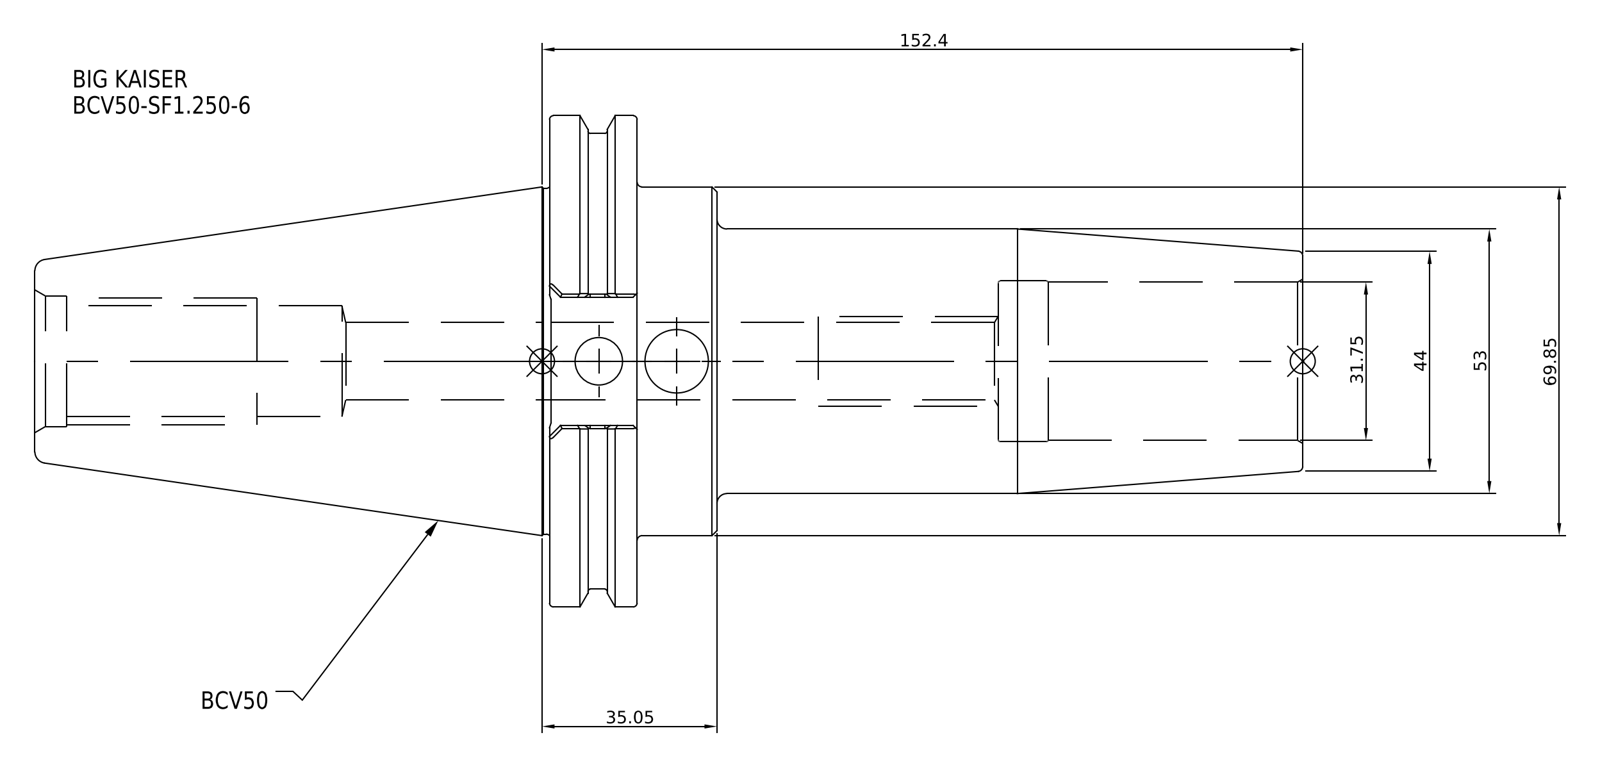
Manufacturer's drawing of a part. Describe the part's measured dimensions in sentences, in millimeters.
The part is named "BCV50-SF1_250-6". Its 3-D file was written by "SolidWorks 2021 (CONFIG_CONTROL_DESIGN)". It is 1 solid with 30 faces: 8 planar, 14 cylindrical and 8 other. Overall it measures 254 by 98.43 by 98.43 millimeters. Its volume is 640 981 cubic millimeters and its surface area 64 143 square millimeters. Round holes: 1 of diameter 31.75. Round bosses or shafts: 1 of diameter 98.43, 1 of diameter 91.29, 1 of diameter 69.85, 1 of diameter 53. The main face-to-face distances are 17.55, 16, 33.55, 136.65, 120.65, 103.1, 66.35, 82.35, 99.9, 203.
